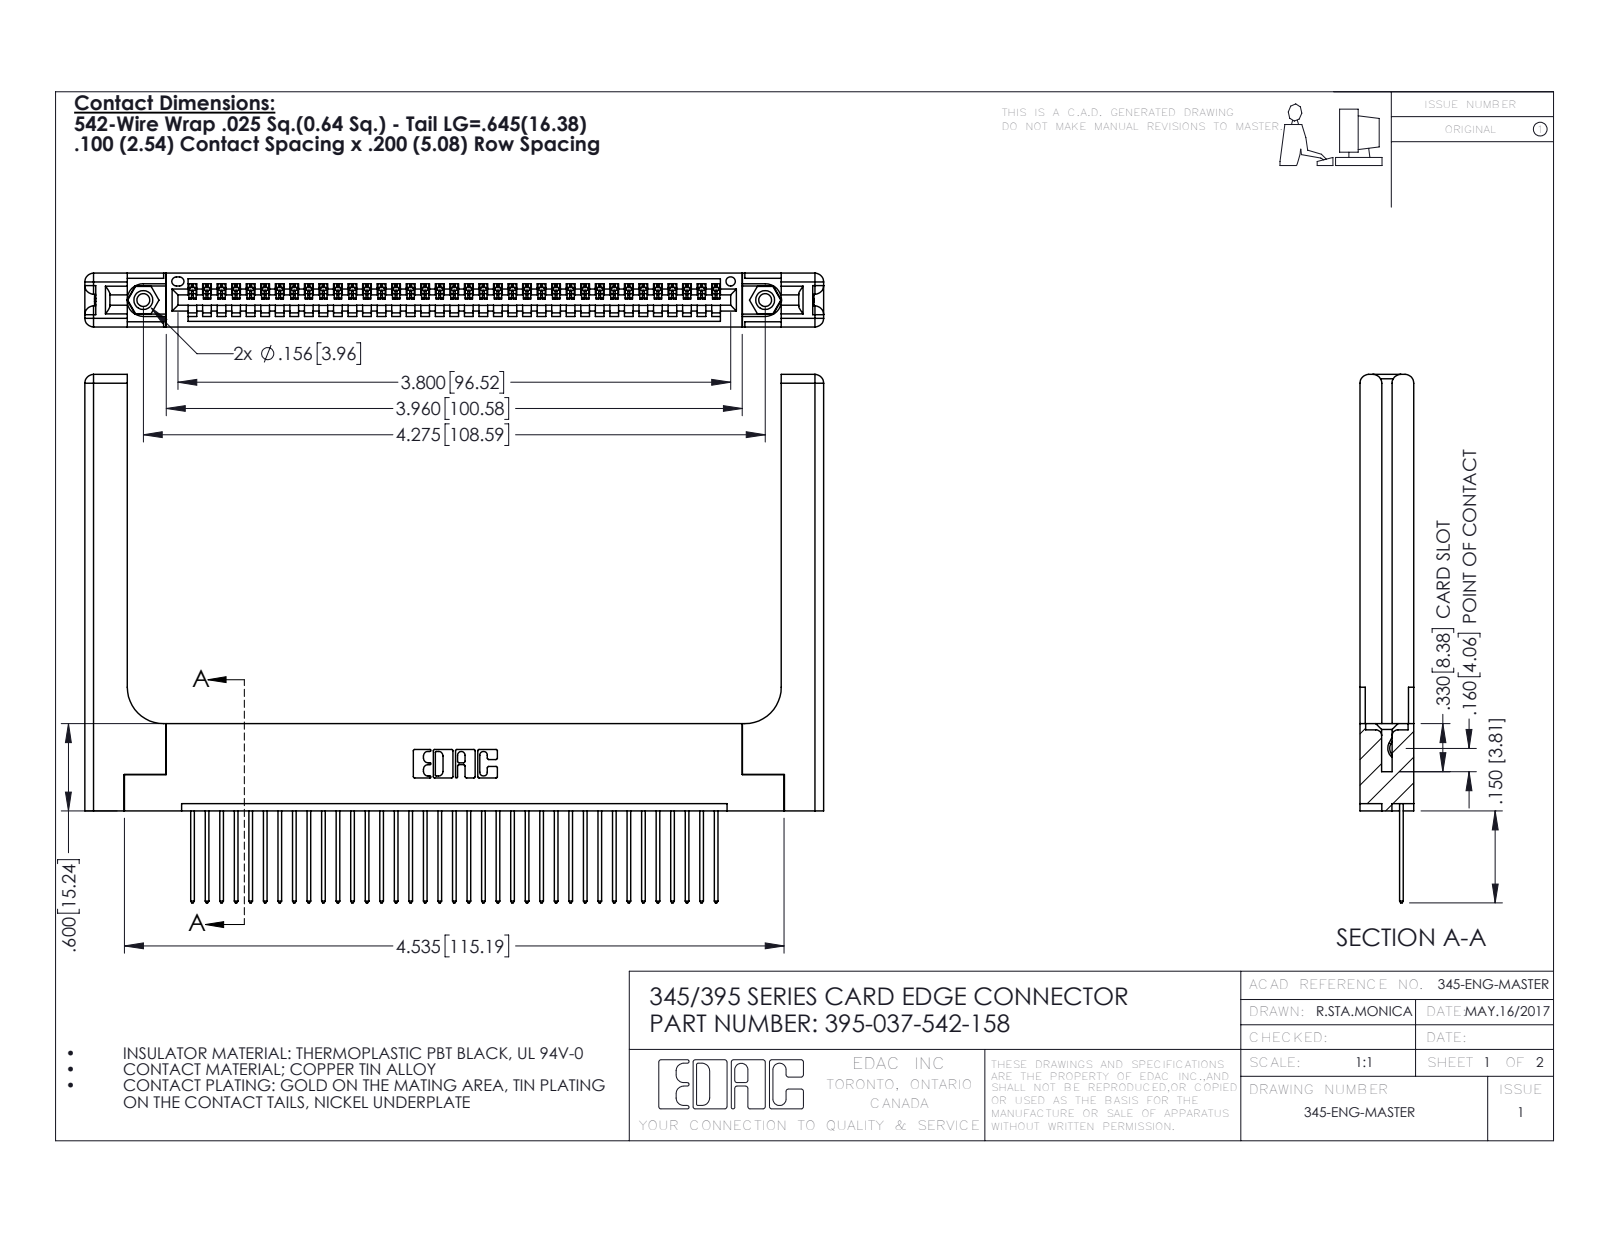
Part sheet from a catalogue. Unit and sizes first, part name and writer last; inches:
Units: inches
Overall size (bounding box): 5.079 × 3.632 × 0.37
Round holes (diameter × count): ⌀0.089 ×2, ⌀0.125 ×2, ⌀0.156 ×2, ⌀0.064 ×1
Round bosses / shafts (diameter × count): ⌀0.155 ×2
Partial cylindrical surfaces — rounded edges, fillets, slot ends (radius × count): R0.006 ×74, R0.01 ×74, R0.01 ×22, R0.06 ×16, R0.007 ×6, R0.031 ×6, R0.026 ×3, R0.03 ×2
Main face-to-face distances: 0.072, 0.37, 0.298, 0.098, 0.272, 0.025, 0.2, 0.148, 0.15, 0.225
Hole centre spacings: 0.27, 4.039, 4.275
Volume: 1.269 in³ · Surface area: 34.25 in²
Bodies: 42 solids, 2528 faces (1708 planar, 760 cylindrical, 60 other)
Part name (STEP PRODUCT): 345-292-001_345-293-142; 395-037-542-158; 345-250-001_345-250-001-102; 345 Part_Flush Mounting Lugs - 0.156 Dia-TH (+1 more)
STEP written by: SolidWorks 2016 (CONFIG_CONTROL_DESIGN)
